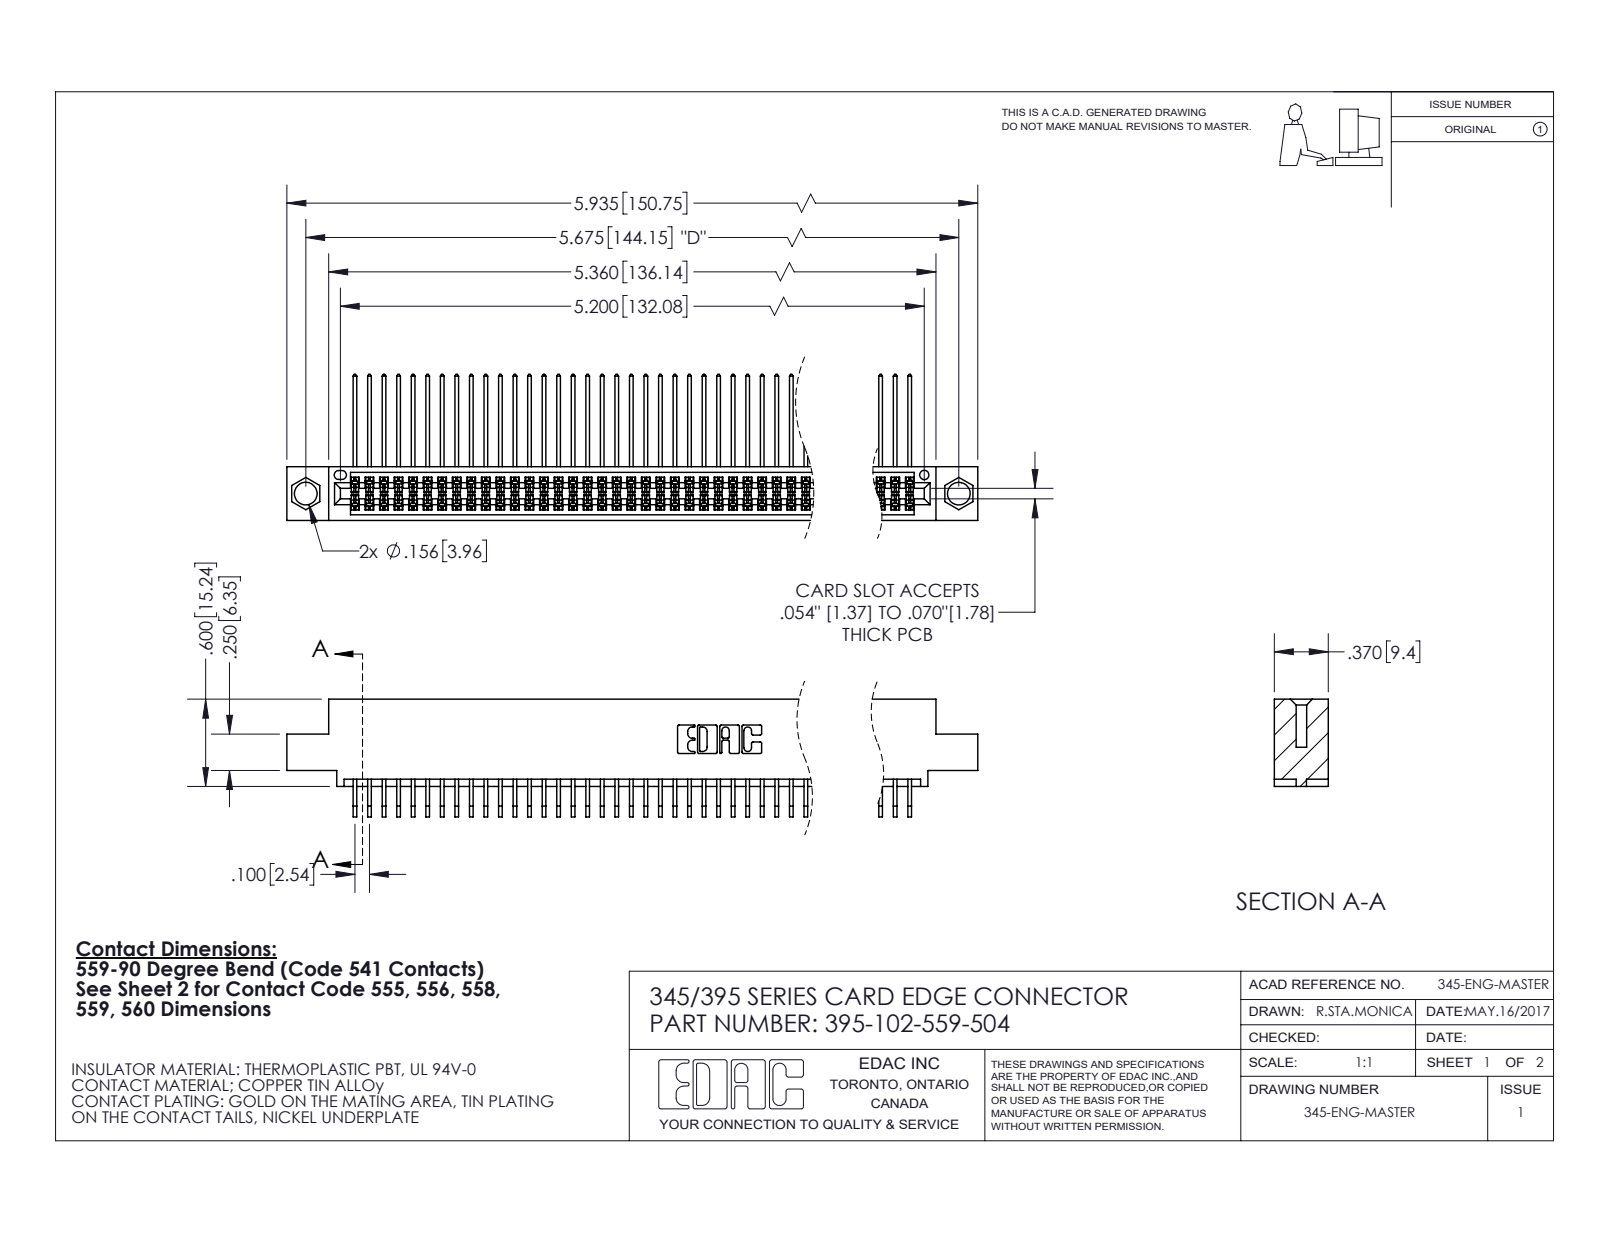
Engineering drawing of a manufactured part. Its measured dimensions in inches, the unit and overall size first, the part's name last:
Units: inches
Overall size (bounding box): 5.935 × 1.005 × 0.809
Round holes (diameter × count): ⌀0.156 ×2, ⌀0.064 ×1
Partial cylindrical surfaces — rounded edges, fillets, slot ends (radius × count): R0.006 ×204, R0.01 ×22, R0.007 ×6, R0.031 ×6, R0.026 ×3, R0.014 ×2, R0.019 ×2, R0.022 ×2
Main face-to-face distances: 0.072, 0.298, 0.2, 0.37, 0.098, 0.272, 0.025, 0.225, 0.175, 0.15
Hole centre spacings: 0.27, 5.439, 5.675
Volume: 0.924 in³ · Surface area: 39.15 in²
Bodies: 103 solids, 5448 faces (3668 planar, 1780 cylindrical, 0 other)
Part name (STEP PRODUCT): 345-292-001_559 Tail - 2; 345 Part_0.110 Offset - 0.156 Dia-TI; 395-102-559-504; 345-292-001_558 559 Tail - 1
STEP written by: SolidWorks 2020 (CONFIG_CONTROL_DESIGN)
